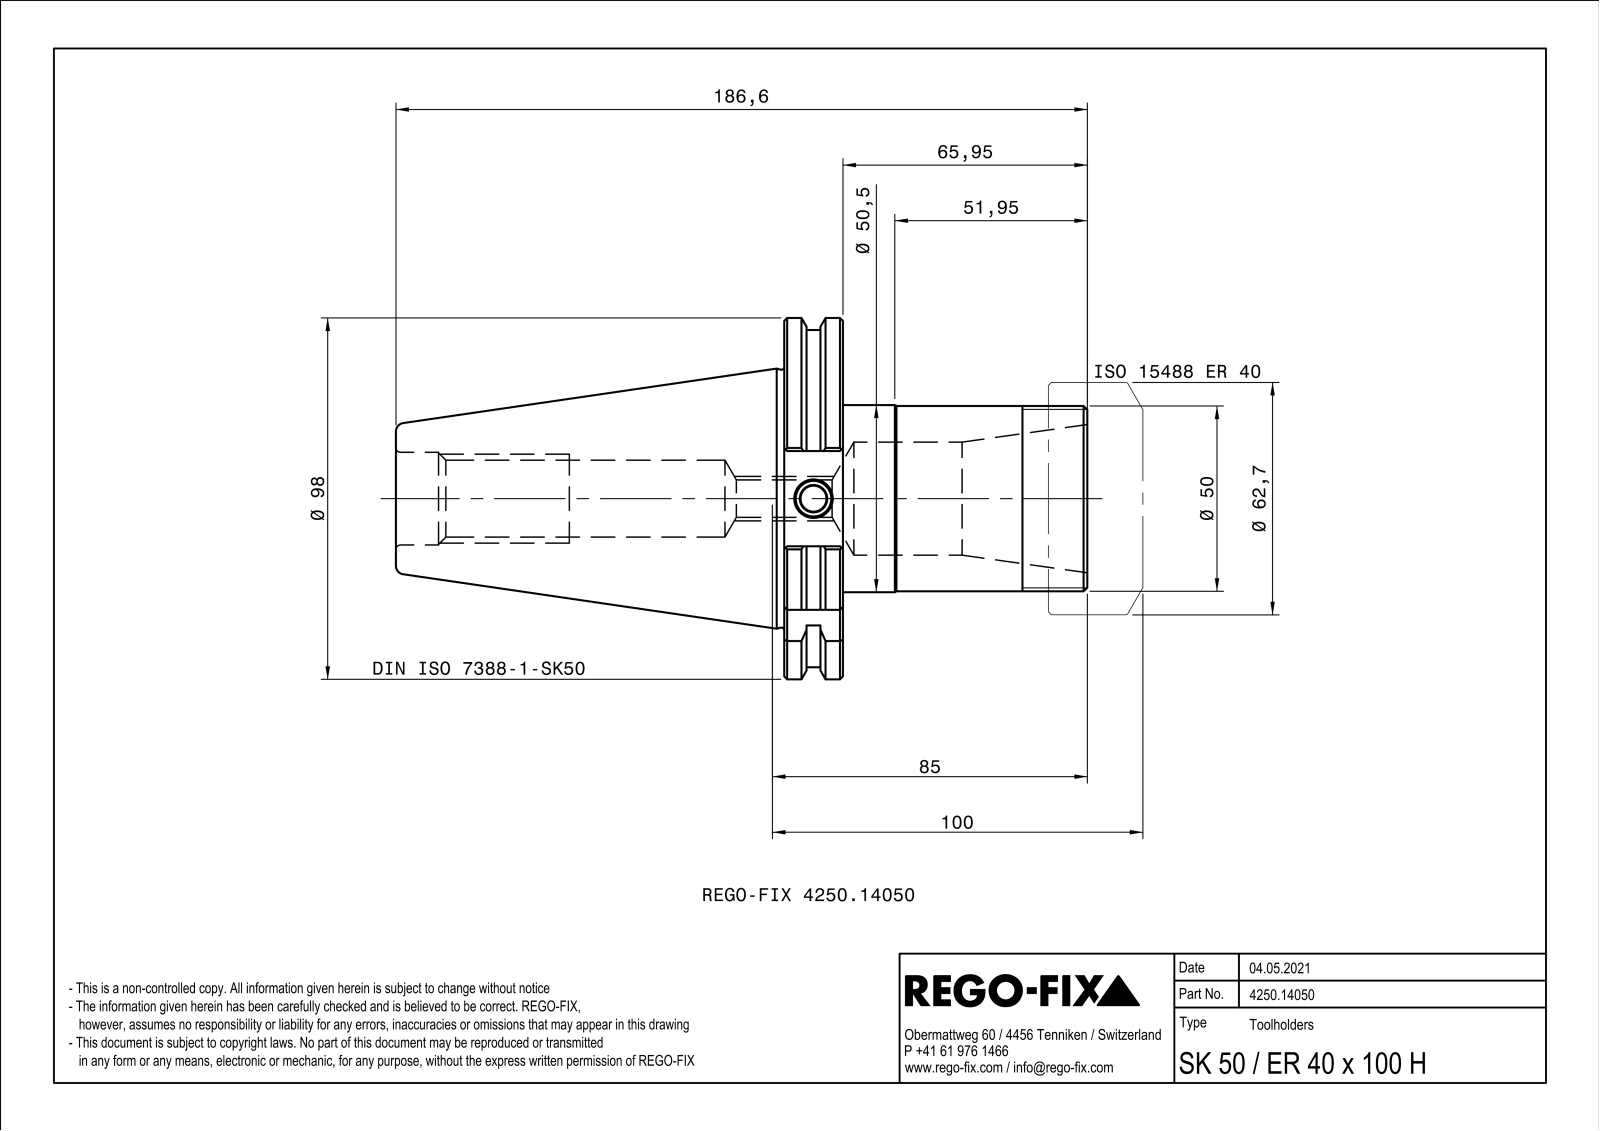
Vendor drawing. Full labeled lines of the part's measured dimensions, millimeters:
Part name (STEP PRODUCT): NOCUT
STEP written by: SIEMENS PLM Software Solid Edge ST10 (AUTOMOTIVE_DESIGN)
Units: millimetres
Bodies: 1 solid, 126 faces (41 planar, 36 cylindrical, 49 other)
Overall size (bounding box): 186.6 × 97.5 × 93.58
Volume: 401 493 mm³ · Surface area: 59 243 mm²
Round holes (diameter × count): ⌀3.5 ×5, ⌀7 ×1, ⌀10 ×1, ⌀10.11 ×1, ⌀20.75 ×1, ⌀25 ×1, ⌀30.5 ×1
Round bosses / shafts (diameter × count): ⌀50.5 ×1, ⌀50 ×1
Partial cylindrical surfaces — rounded edges, fillets, slot ends (radius × count): R0.5 ×5, R45.5 ×1, R48.75 ×1
Main face-to-face distances: 15.85, 65.95, 81.8, 186.6, 120.65, 104.8, 72.8, 25.7, 72.03, 6.08
